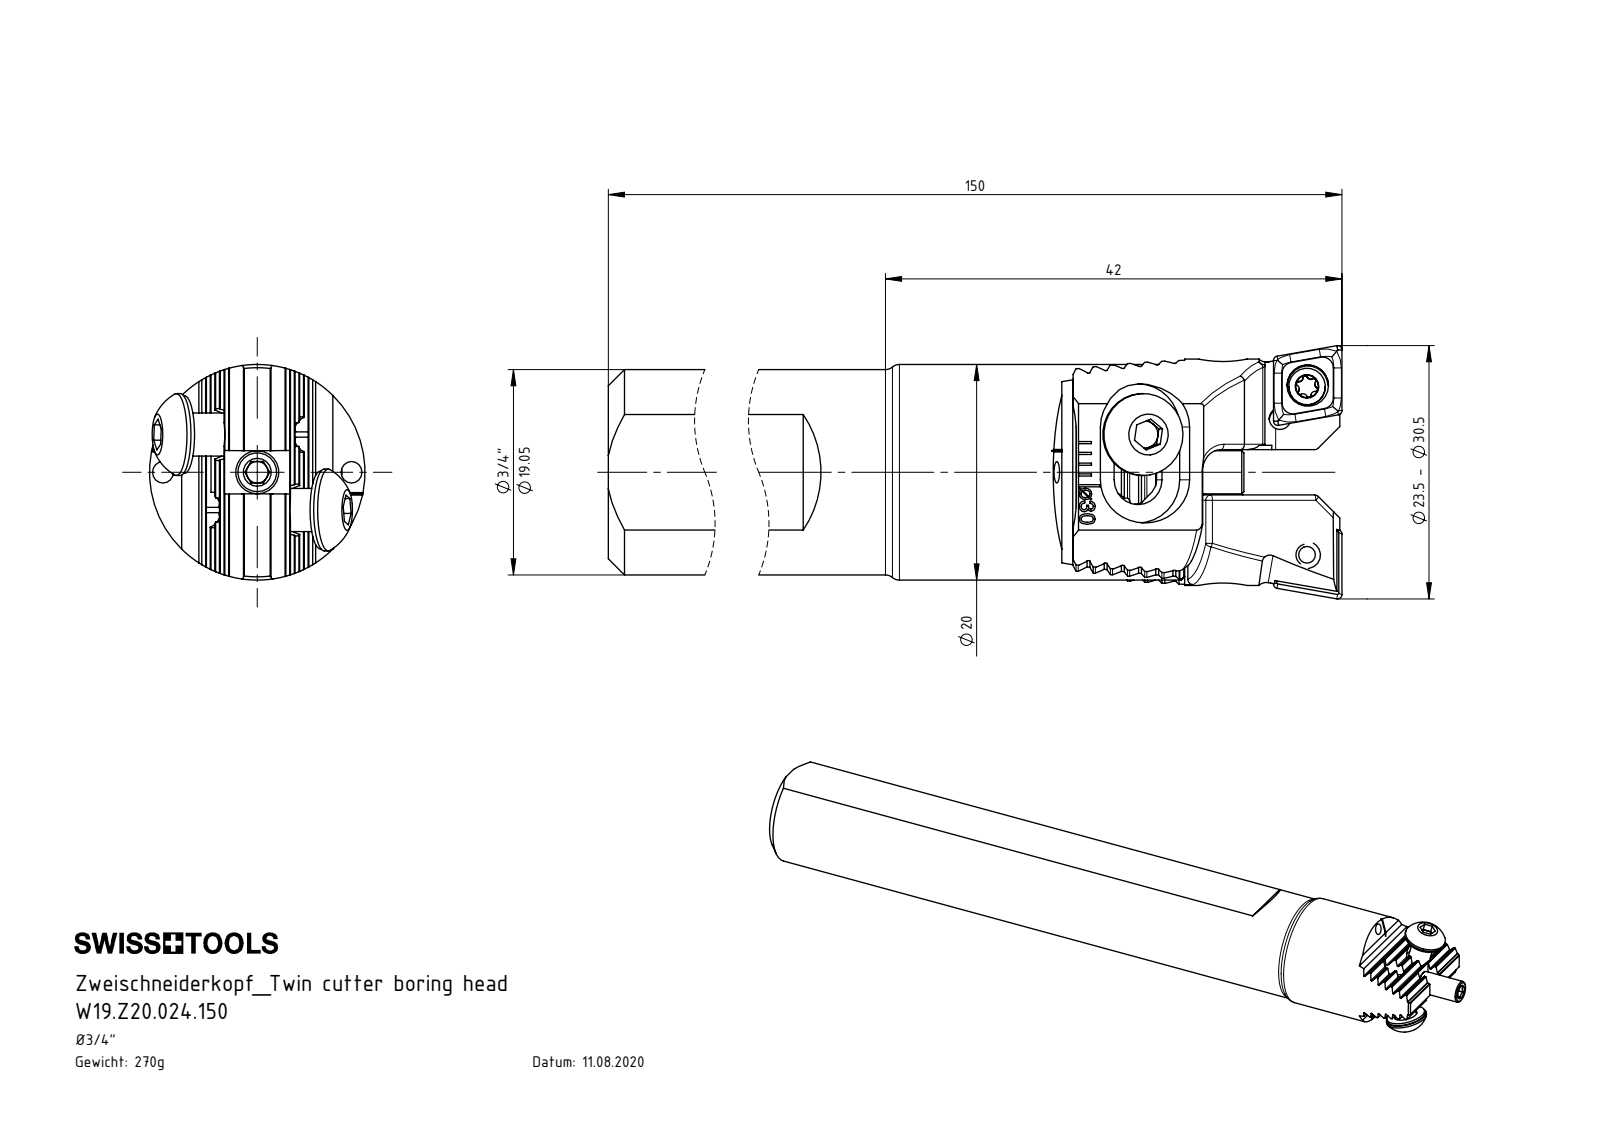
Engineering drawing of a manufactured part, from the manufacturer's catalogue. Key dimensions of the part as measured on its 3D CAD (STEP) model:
Part name (STEP PRODUCT): W19.Z20.K23.150; Z20-ER1.001.008; Z20-ER1.002.008_A; W19-Z20.K23.150_A (+2 more)
STEP written by: SolidWorks 2017 (AUTOMOTIVE_DESIGN)
Units: millimetres
Bodies: 6 solids, 243 faces (152 planar, 62 cylindrical, 29 other)
Overall size (bounding box): 140.9 × 20 × 20
Volume: 31 654 mm³ · Surface area: 12 309 mm²
Round holes (diameter × count): ⌀2 ×4, ⌀3.3 ×2, ⌀4.3 ×2, ⌀5 ×2, ⌀2.5 ×1, ⌀7 ×1
Round bosses / shafts (diameter × count): ⌀4 ×3, ⌀7.6 ×2, ⌀7.2 ×2, ⌀20 ×1, ⌀19.05 ×1, ⌀3 ×1, ⌀2.2 ×1
Partial cylindrical surfaces — rounded edges, fillets, slot ends (radius × count): R0.12 ×14, R220 ×2
Main face-to-face distances: 1.43, 4.28, 5.71, 2.86, 2.85, 7.14, 1.42, 0.4, 124, 3.6
